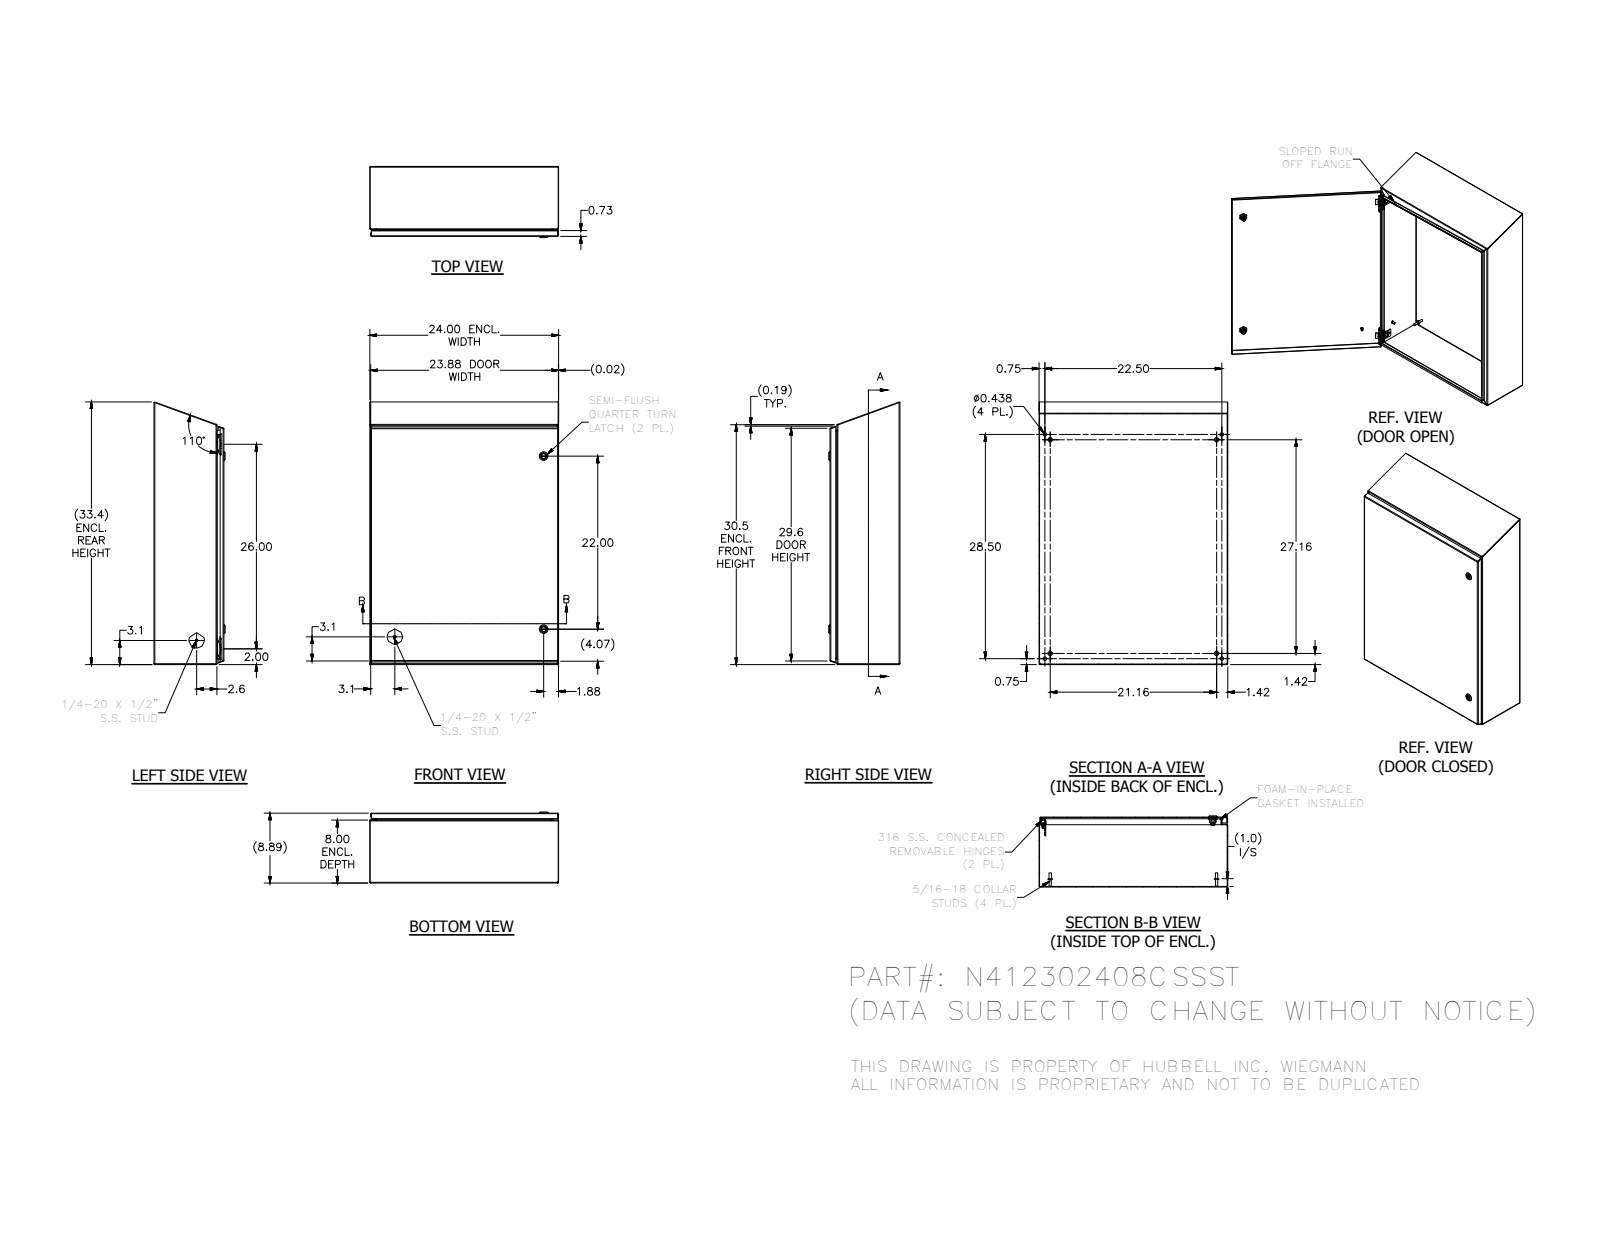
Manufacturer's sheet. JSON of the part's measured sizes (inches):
{"part_name": "N412_CSSST-assm; N412302408CSSSTB3S; HFW3161; HFW328176 (+8 more)", "step_written_by": "Autodesk Inventor 2012 (AUTOMOTIVE_DESIGN)", "units": "inches", "bodies": {"solids": 42, "faces": 1732, "planar": 717, "cylindrical": 604, "other": 411}, "overall_size": [33.391, 24, 9.044], "volume_in3": 196.2, "surface_area_in2": 5337, "round_holes": [[0.093, 4], [0.152, 4], [0.167, 4], [0.172, 4], [0.187, 4], [0.437, 4], [0.156, 3], [0.197, 2], [0.315, 2], [0.394, 2], [0.402, 2], [0.634, 2]], "round_bosses_or_shafts": [[0.25, 10], [0.563, 4], [0.36, 4], [0.32, 4], [0.3, 4], [0.275, 4], [0.256, 4], [0.164, 4]], "partial_cylinders_radius": [[0.031, 29], [0.05, 26], [0.02, 24], [0.105, 19], [0.016, 18], [0.125, 16], [0.032, 8], [0.177, 6]], "face_to_face_distances": [0.074, 8.813, 8.887, 8.739, 23.926, 23.852, 24, 7.926, 0.887, 0.813], "hole_center_spacings": [26, 22.8, 0.5, 0.656, 0.66, 0.952, 1.307, 1.311]}
